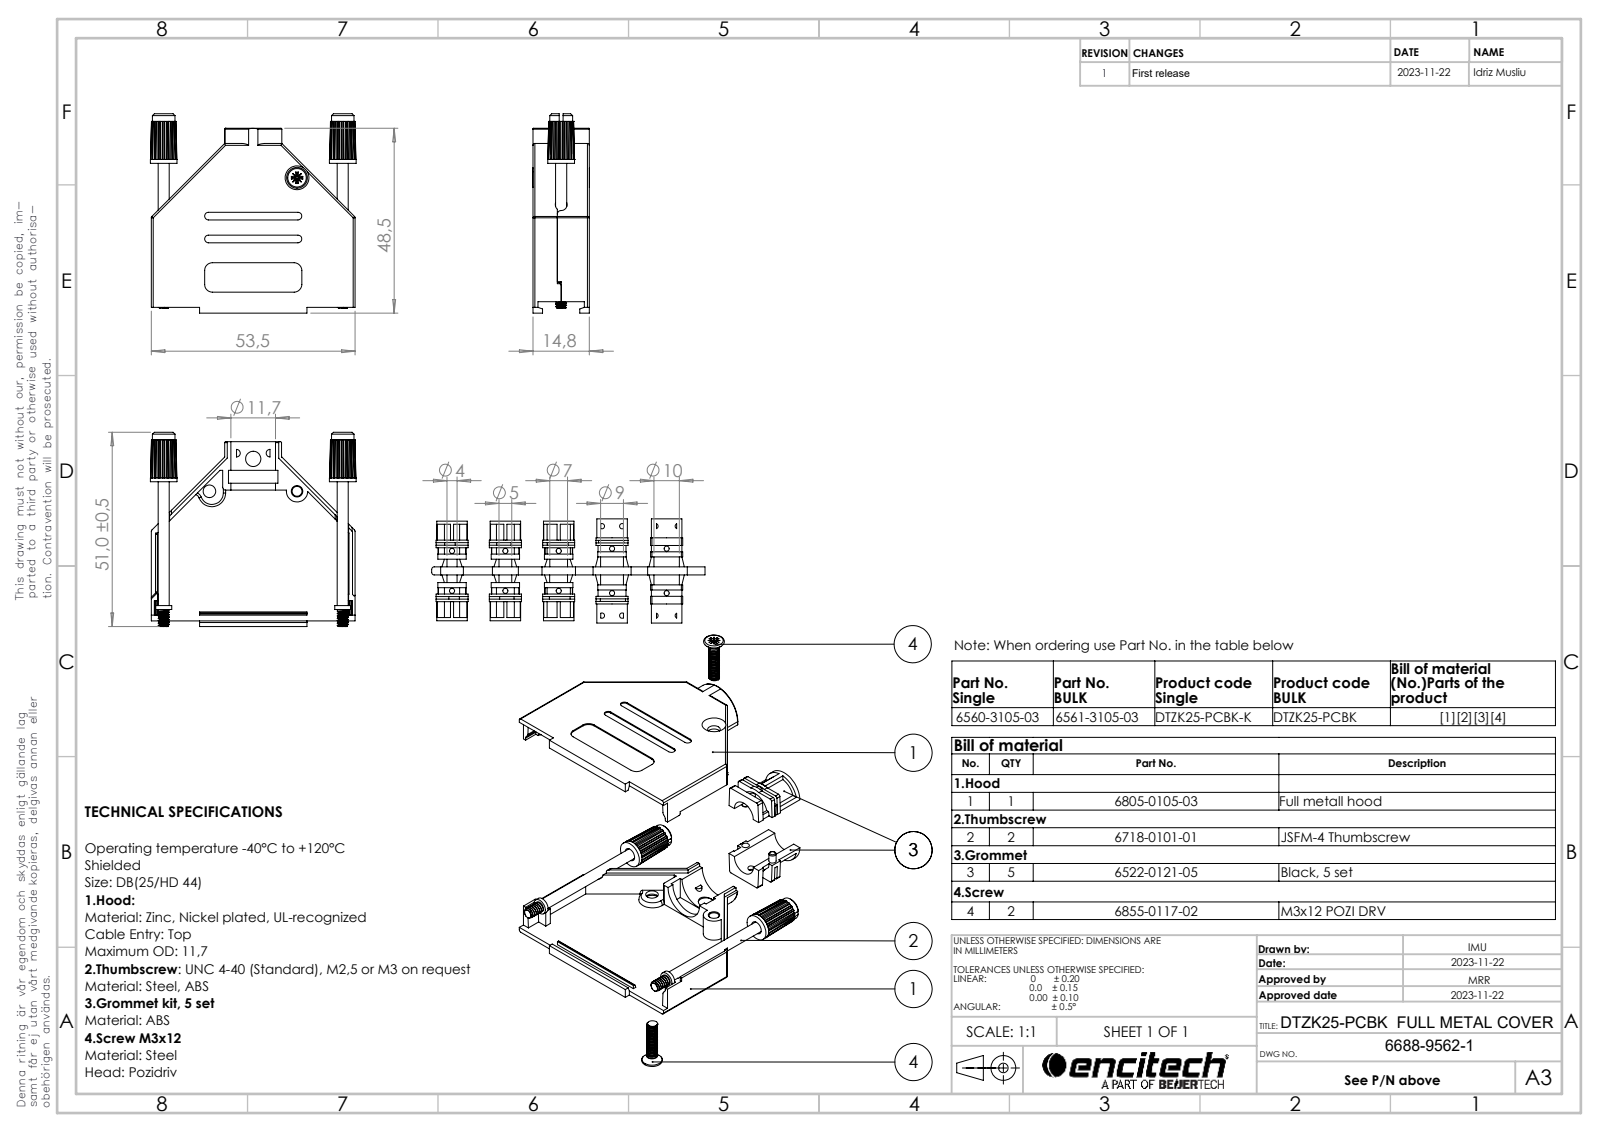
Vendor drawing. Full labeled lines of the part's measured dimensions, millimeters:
Part name (STEP PRODUCT): 6805-0105-03; 6718-0101-01; 6688-9562-1; 6855-0117-02 (+1 more)
STEP written by: SolidWorks 2021 (AUTOMOTIVE_DESIGN)
Units: millimetres
Bodies: 8 solids, 870 faces (508 planar, 254 cylindrical, 108 other)
Overall size (bounding box): 54 × 52.3 × 14.85
Volume: 10 432 mm³ · Surface area: 15 750 mm²
Round holes (diameter × count): ⌀2 ×3, ⌀2.6 ×2, ⌀3.1 ×2, ⌀3.3 ×2, ⌀4 ×1, ⌀7 ×1, ⌀11.7 ×1
Round bosses / shafts (diameter × count): ⌀2.9 ×4, ⌀7 ×2, ⌀6 ×2, ⌀4.2 ×2, ⌀1.9 ×2, ⌀15 ×1, ⌀11.6 ×1, ⌀9.2 ×1
Partial cylindrical surfaces — rounded edges, fillets, slot ends (radius × count): R0.5 ×24, R1 ×12, R0.1 ×8, R0.25 ×8, R0.2 ×6, R2 ×4, R5.91 ×4, R0.3 ×2
Main face-to-face distances: 1.3, 13.5, 14.8, 12.2, 6.1, 1.6, 1, 7.4, 7.1, 14.5
Hole centre spacings: 5.71, 6.97, 7.45, 11.54, 14.3, 16.9, 23.5, 7.6
